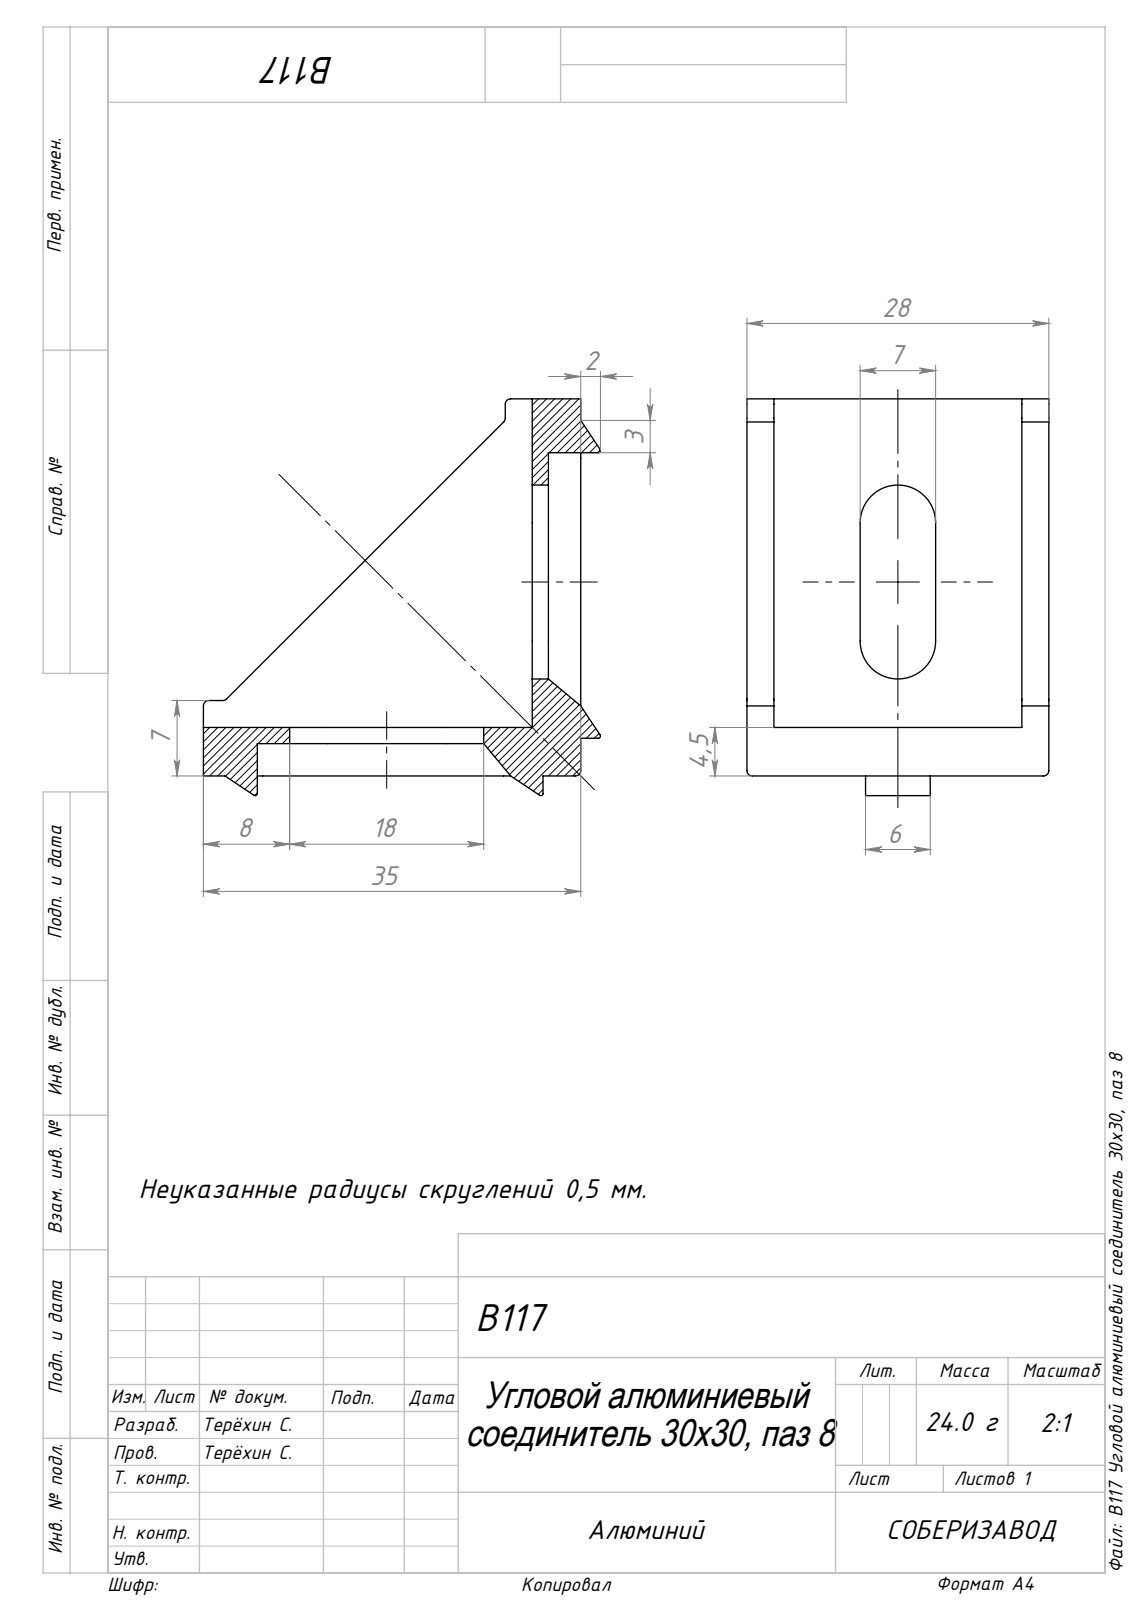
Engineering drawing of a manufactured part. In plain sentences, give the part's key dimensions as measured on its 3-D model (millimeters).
The part is named "B117 Угловой алюминиевый соединитель 30х30, паз 8". Its 3-D file was written by "SolidWorks 2026 (CONFIG_CONTROL_DESIGN)". It is 1 solid with 76 faces: 44 planar, 30 cylindrical and 2 other. Overall it measures 36.83 by 36.83 by 28 millimeters. Its volume is 9 390 cubic millimeters and its surface area 6 407 square millimeters. Partial cylindrical surfaces (rounded edges, fillets, slot ends): 17 of radius 0.5, 4 of radius 0.2, 4 of radius 3.5. The main face-to-face distances are 4.5, 25.5, 2.5, 28, 23, 35, 30.5, 10.25, 17.75, 7.75.
